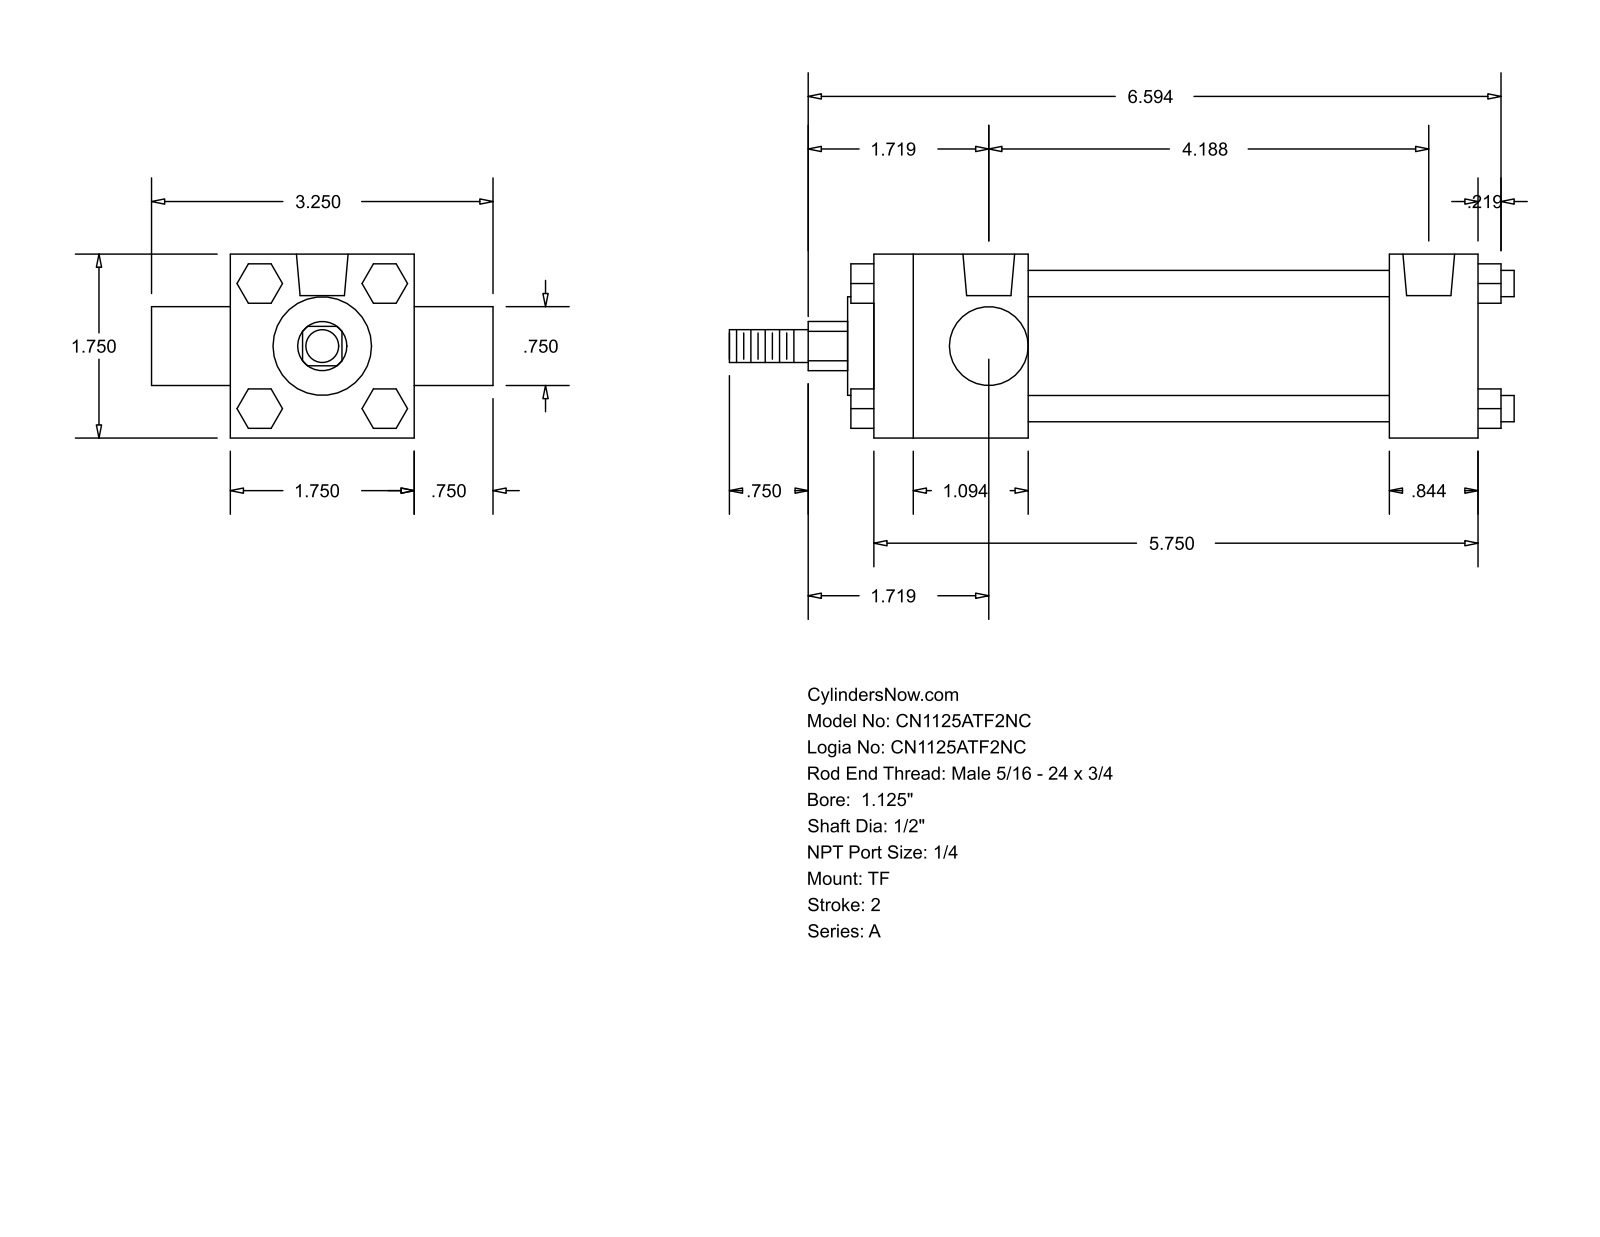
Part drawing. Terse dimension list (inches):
name: A_TF__0112_0.5
written by: GSSL Pune (CONFIG_CONTROL_DESIGN)
unit: in
bodies: 0 solids, 120 faces (92 planar, 28 cylindrical, 0 other)
size: 7.469 × 3.25 × 1.75
holes: 3× ⌀0.219, 2× ⌀0.492
bosses: 4× ⌀0.25, 1× ⌀1.255, 1× ⌀0.937, 1× ⌀0.75, 1× ⌀0.5, 1× ⌀0.313
rounds: 1× R0.234
face distances: 1.75, 5.75, 4.906, 0.844, 1.469, 3.437, 4.281, 0.75, 2.5, 0.375
hole spacings: 0.062, 0.063, 4.063, 4.125, 4.125, 4.187
